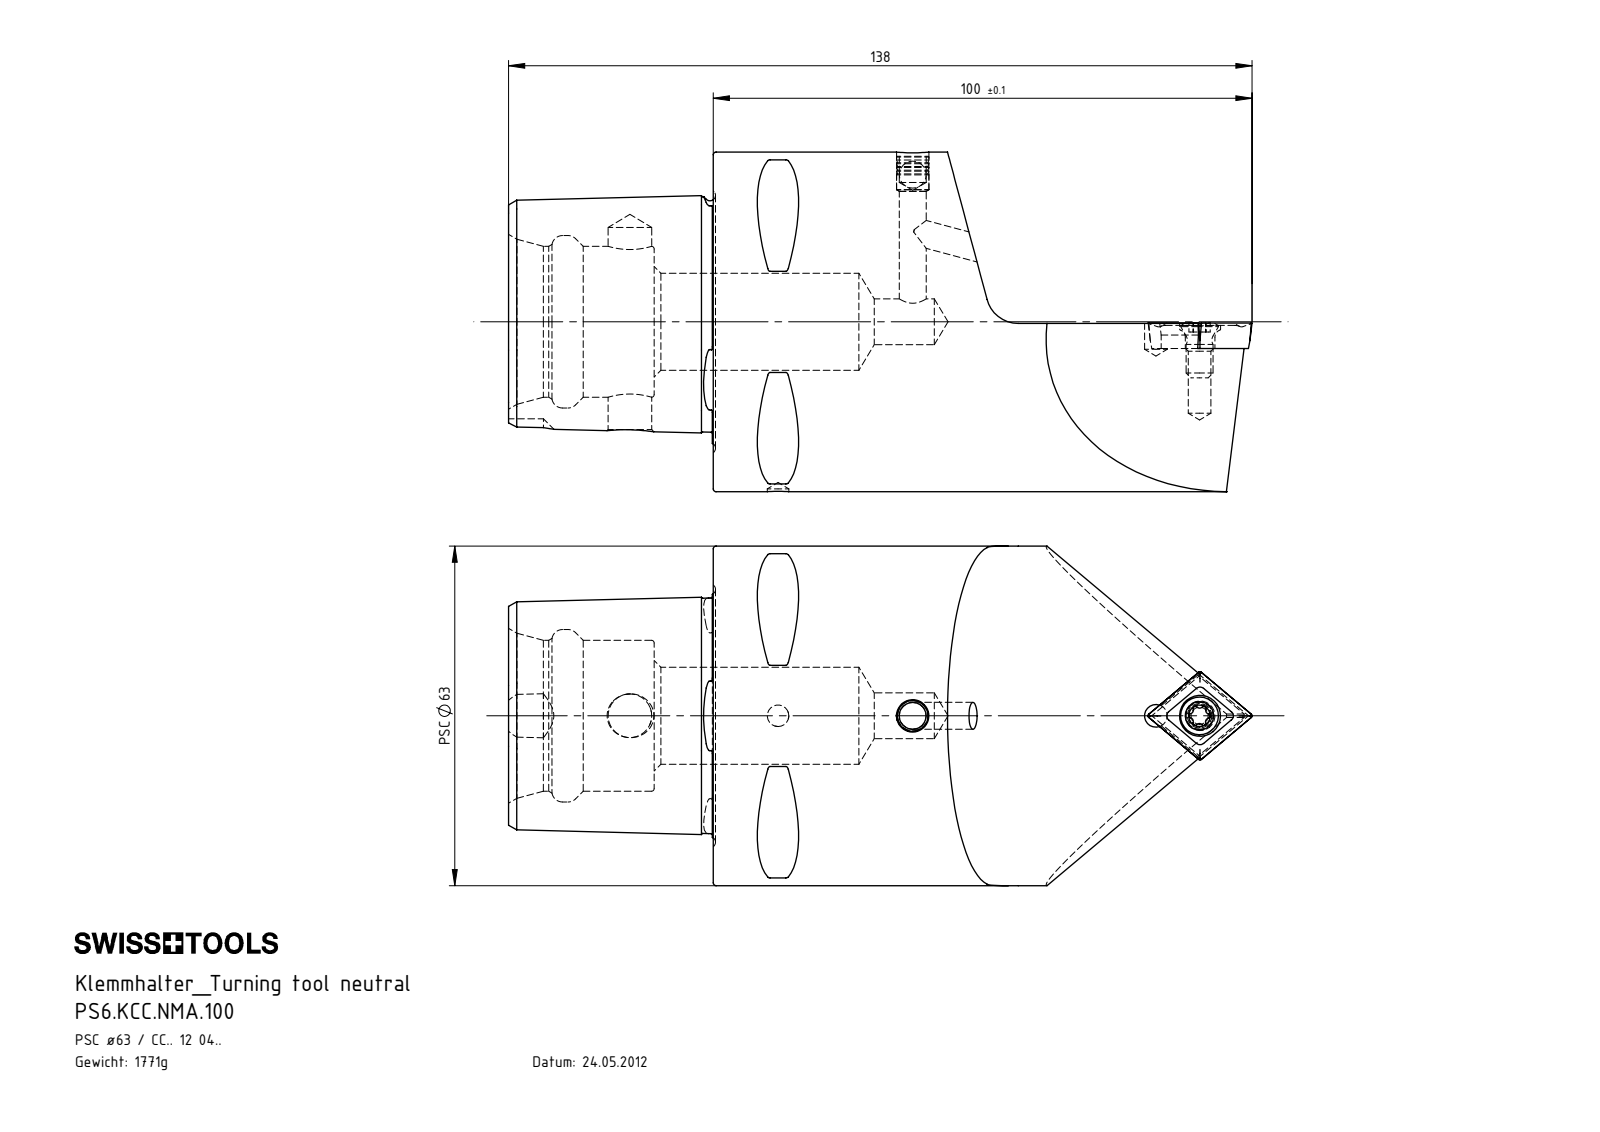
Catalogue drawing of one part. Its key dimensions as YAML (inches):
part_name: "PS6-KCC.NMA.100; KVT_MB_600_060; WCC-ER2.001.010_A; CCMT120404 (+1 more)"
step_written_by: "SolidWorks 2012 (CONFIG_CONTROL_DESIGN)"
units: inches
bodies: {solids: 5, faces: 262, planar: 48, cylindrical: 67, other: 147}
overall_size: [5.433, 2.48, 2.48]
volume: 13.76
surface_area: 50.97
round_holes:
  - {diameter: 0.165, count: 2}
  - {diameter: 0.197, count: 2}
  - {diameter: 0.157, count: 1}
  - {diameter: 0.217, count: 1}
  - {diameter: 0.299, count: 1}
  - {diameter: 0.319, count: 1}
  - {diameter: 0.335, count: 1}
  - {diameter: 0.709, count: 1}
  - {diameter: 1.102, count: 1}
  - {diameter: 1.26, count: 1}
round_bosses_or_shafts:
  - {diameter: 2.48, count: 1}
  - {diameter: 0.276, count: 1}
  - {diameter: 0.236, count: 1}
  - {diameter: 0.197, count: 1}
partial_cylinders:
  - {radius: 0.02, count: 8}
  - {radius: 0.015, count: 6}
  - {radius: 0.027, count: 3}
  - {radius: 0.027, count: 3}
  - {radius: 0.236, count: 2}
face_to_face_distances: [1.496, 0.98, 1.063, 0.433, 0.183, 2.197, 1.488, 0.425, 0.187, 1.148]
hole_center_spacings: [0.319, 0.323, 0.984, 1.083, 1.777, 2.067, 2.096, 2.1]
